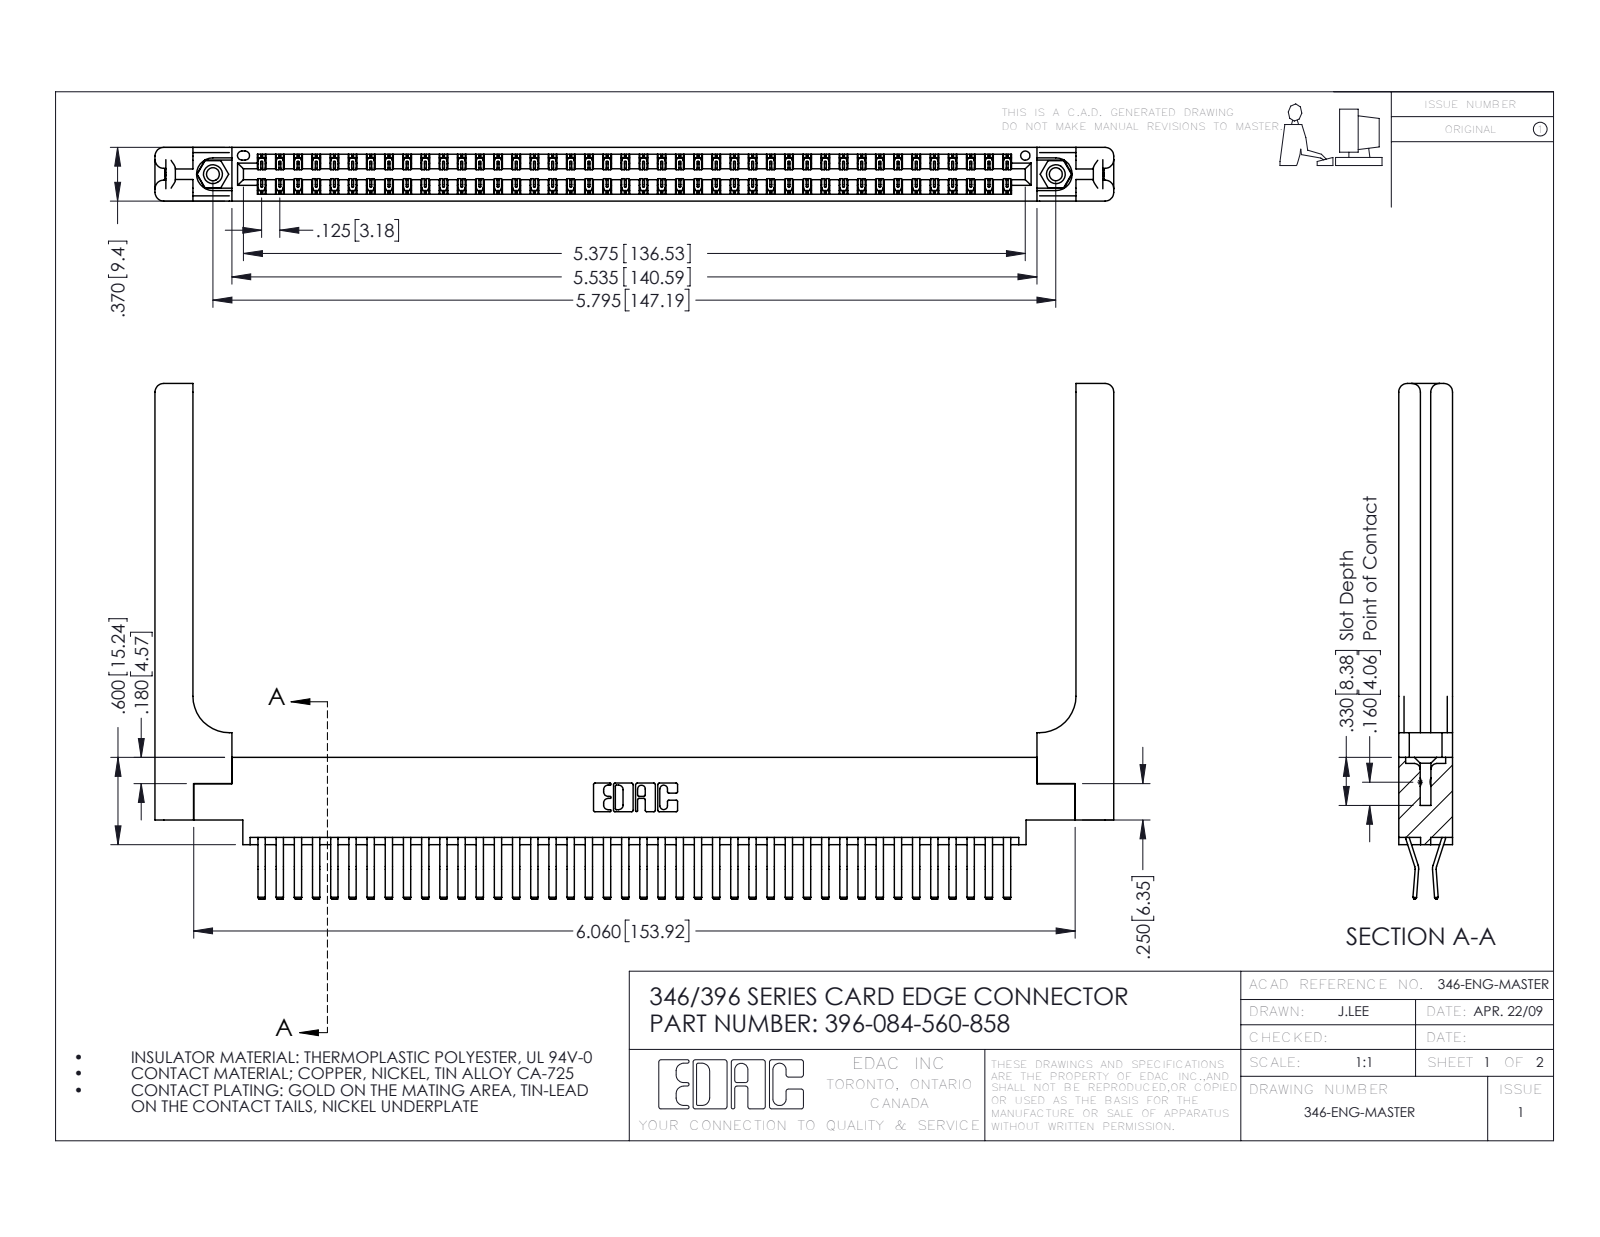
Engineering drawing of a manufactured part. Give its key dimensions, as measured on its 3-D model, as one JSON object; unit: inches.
{"part_name": "396-084-560-858; 345-250-001_345-250-001-102; 345-292-001_560 Tail; 346 Part_0.170 Offset - 0.156 Dia-TH (+1 more)", "step_written_by": "SolidWorks 2016 (CONFIG_CONTROL_DESIGN)", "units": "inches", "bodies": {"solids": 89, "faces": 4918, "planar": 3168, "cylindrical": 1690, "other": 60}, "overall_size": [6.591, 3.545, 0.37], "volume_in3": 1.478, "surface_area_in2": 45.89, "round_holes": [[0.089, 2], [0.125, 2], [0.156, 2], [0.064, 1]], "round_bosses_or_shafts": [[0.155, 2]], "partial_cylinders_radius": [[0.006, 126], [0.01, 22], [0.06, 16], [0.007, 6], [0.031, 6], [0.026, 3], [0.01, 2], [0.014, 2]], "face_to_face_distances": [0.37, 0.048, 0.322, 0.072, 0.025, 0.148, 0.15, 0.25, 0.298, 0.275], "hole_center_spacings": [0.246, 5.586, 5.795]}
